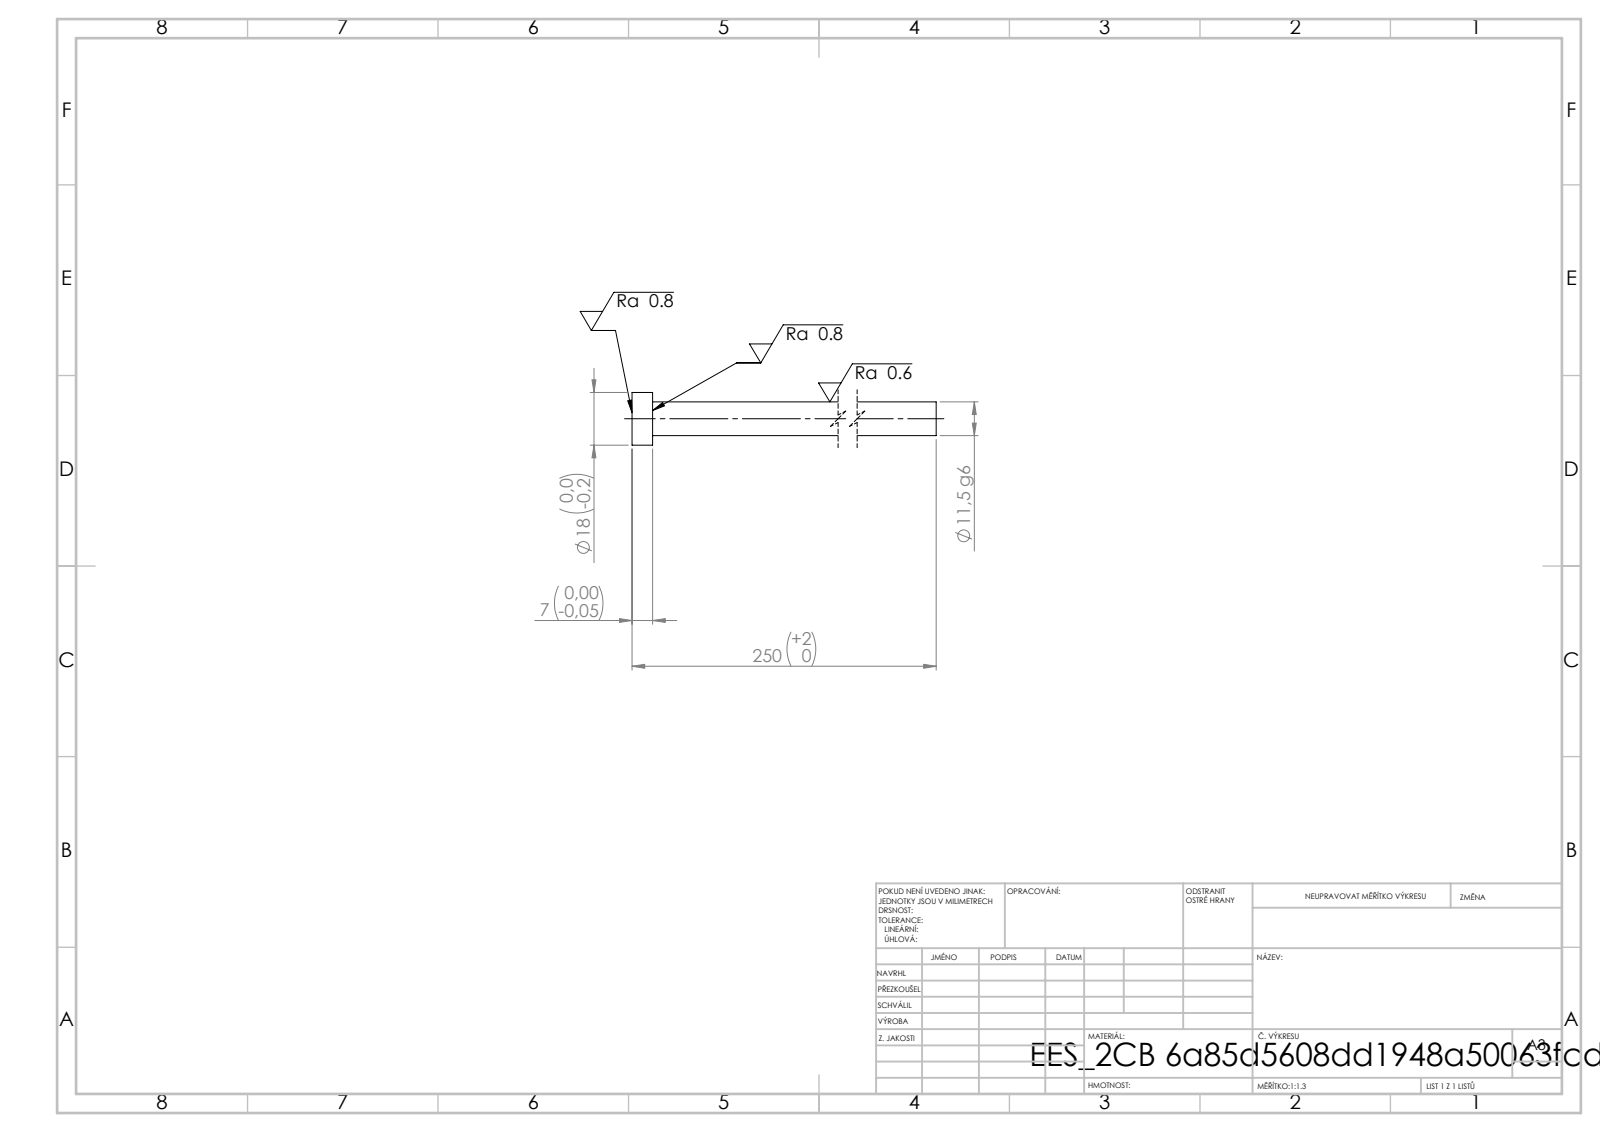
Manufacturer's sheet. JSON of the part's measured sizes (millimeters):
{"step_written_by": "SolidWorks 2019 (CONFIG_CONTROL_DESIGN)", "units": "millimeters", "bodies": {"solids": 1, "faces": 7, "planar": 3, "cylindrical": 4, "other": 0}, "overall_size": [250, 18, 18], "volume_mm3": 27021, "surface_area_mm2": 9684, "round_bosses_or_shafts": [[18, 1], [11.5, 1]], "face_to_face_distances": [7, 250, 243]}
